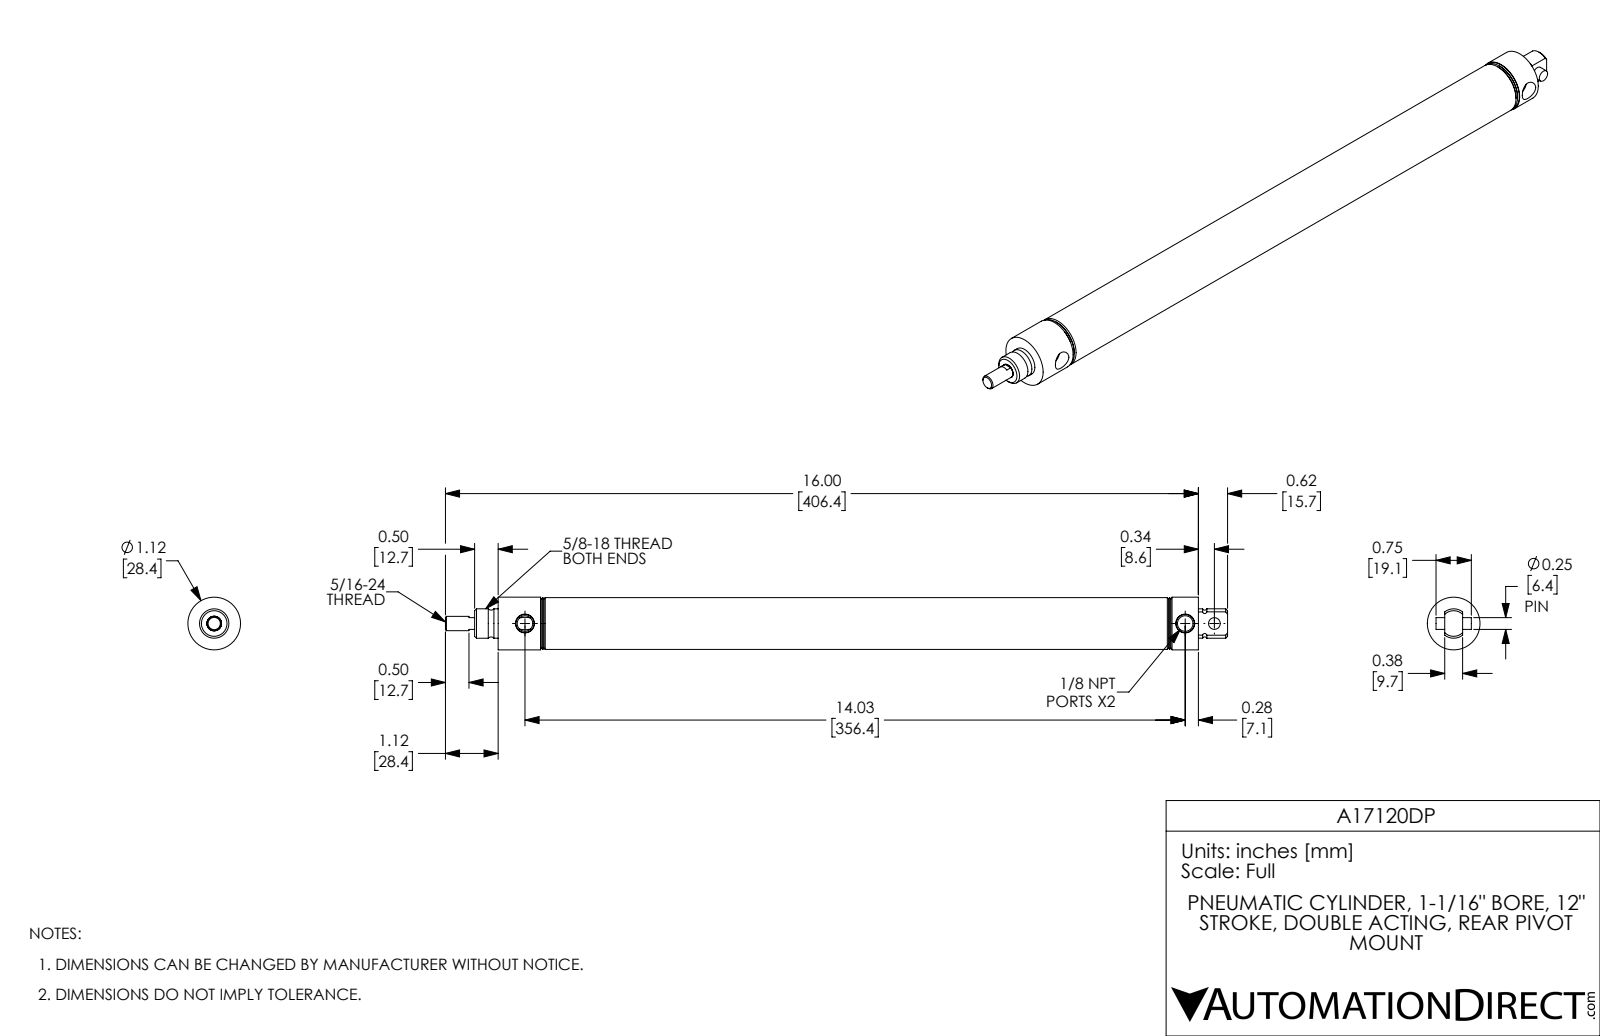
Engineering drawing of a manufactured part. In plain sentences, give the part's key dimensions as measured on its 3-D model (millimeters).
The part is named "A17120DP-MainBody; A17120DP-Rod; A17120DP-PIN; A17120DP". Its 3-D file was written by "SolidWorks 2017 (AUTOMOTIVE_DESIGN)". It is 3 solids with 92 faces: 22 planar, 32 cylindrical and 38 other. Overall it measures 422.1 by 28.4 by 28.4 millimeters. Its volume is 77 150 cubic millimeters and its surface area 77 420 square millimeters. Round holes: 2 of diameter 8.4, 1 of diameter 6.4, 1 of diameter 7.9, 1 of diameter 27. Round bosses or shafts: 1 of diameter 28.4, 1 of diameter 27.9, 1 of diameter 15.9, 1 of diameter 15.8, 1 of diameter 7.7. Partial cylindrical surfaces (rounded edges, fillets, slot ends): 1 of radius 8. The main face-to-face distances are 12.7, 347.7, 317.5, 304.8, 30.2, 42.9, 347.7, 378, 335, 30.2. The hole center spacings are 15.7, 356.4, 372.1.
